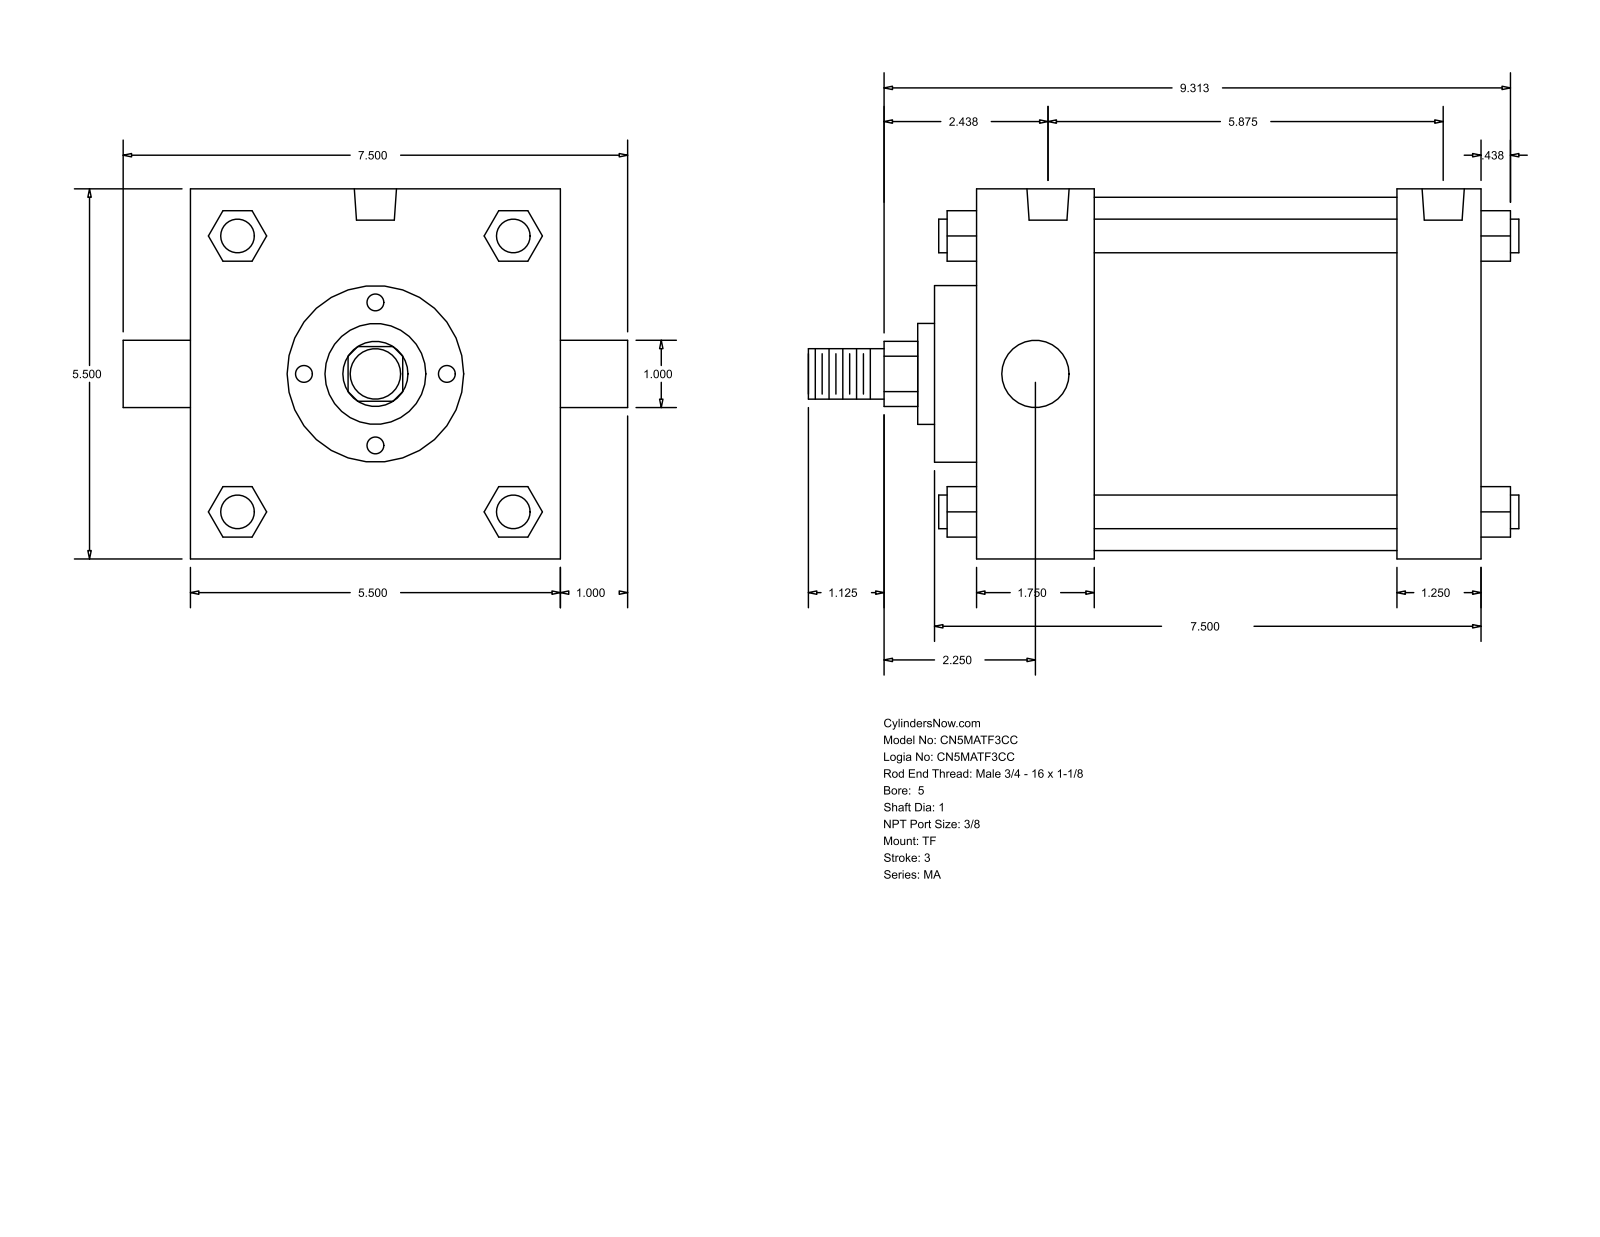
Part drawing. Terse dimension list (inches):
name: MA_TF__0500_1
written by: GSSL Pune (CONFIG_CONTROL_DESIGN)
unit: in
bodies: 0 solids, 122 faces (93 planar, 29 cylindrical, 0 other)
size: 10.563 × 7.5 × 5.5
holes: 3× ⌀0.437, 2× ⌀0.627
bosses: 4× ⌀0.5, 2× ⌀1, 1× ⌀5.25, 1× ⌀2.625, 1× ⌀1.5, 1× ⌀0.75
rounds: 1× R0.484
face distances: 5.5, 7.5, 6.25, 1.25, 1.75, 4.5, 5.75, 0.625, 2.375, 6.875
hole spacings: 0.187, 5.688, 5.5, 5.875
